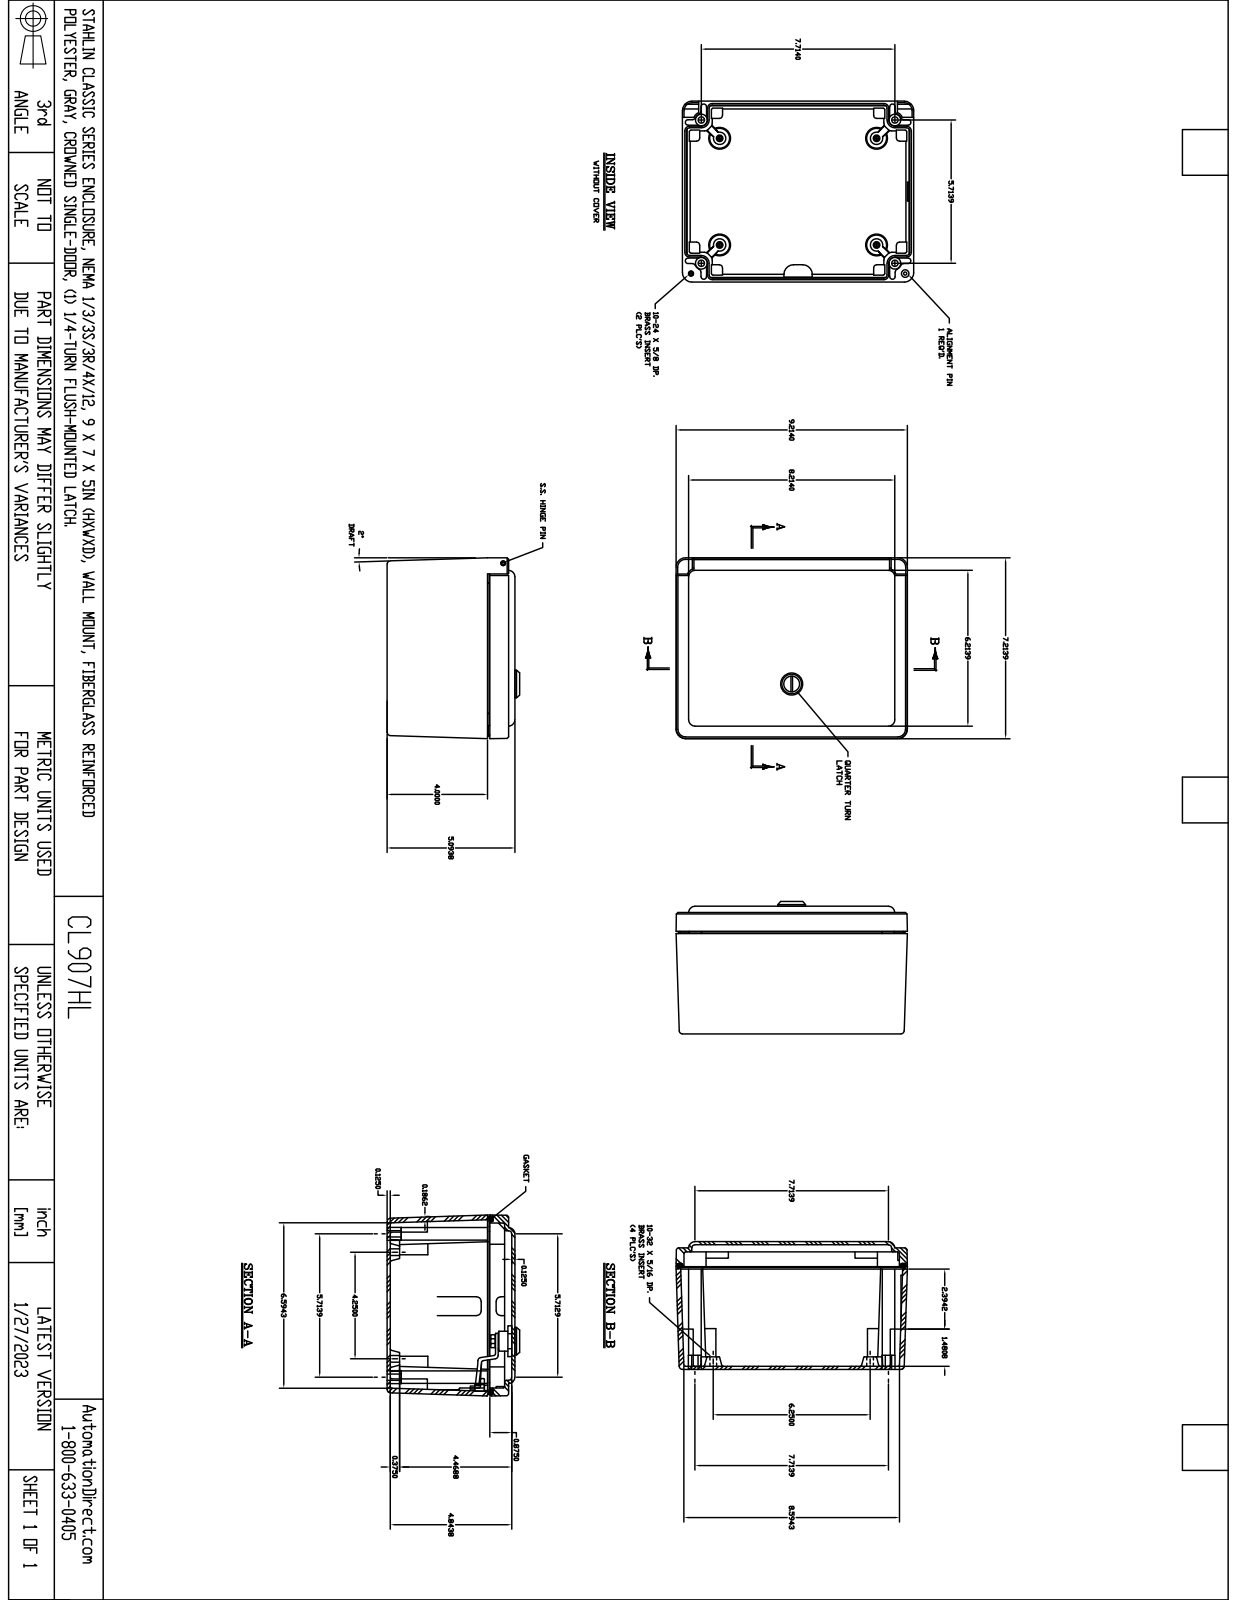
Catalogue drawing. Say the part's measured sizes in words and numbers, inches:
The part is named "CE907HL". Its 3-D file was written by "SolidWorks 2018 (AUTOMOTIVE_DESIGN)". It is 27 solids with 1054 faces: 430 planar, 313 cylindrical and 311 other. Overall it measures 9.22 by 7.22 by 5.281 inches. Its volume is 57.92 cubic inches and its surface area 663.3 square inches. Round holes: 6 of diameter 0.281, 4 of diameter 0.156, 4 of diameter 0.313, 4 of diameter 0.531, 2 of diameter 0.096, 2 of diameter 0.104, 2 of diameter 0.13, 2 of diameter 0.14, 2 of diameter 0.145, 2 of diameter 0.156, 2 of diameter 0.219, 2 of diameter 0.23. Round bosses or shafts: 2 of diameter 0.375, 2 of diameter 0.234, 2 of diameter 0.095, 1 of diameter 1.094, 1 of diameter 0.63, 1 of diameter 0.4, 1 of diameter 0.371, 1 of diameter 0.299. Partial cylindrical surfaces (rounded edges, fillets, slot ends): 60 of radius 0.031, 38 of radius 0.125, 24 of radius 0.063, 11 of radius 0.313, 8 of radius 0.059, 8 of radius 0.062, 8 of radius 0.188, 8 of radius 0.25. The main face-to-face distances are 0.125, 4.969, 0.186, 5.094, 4.844, 0.125, 0.25, 4.844, 4.719, 0.75. The hole center spacings are 1.039, 5.04, 7.024, 8.583, 0.75, 4.651, 0.528, 0.572.
